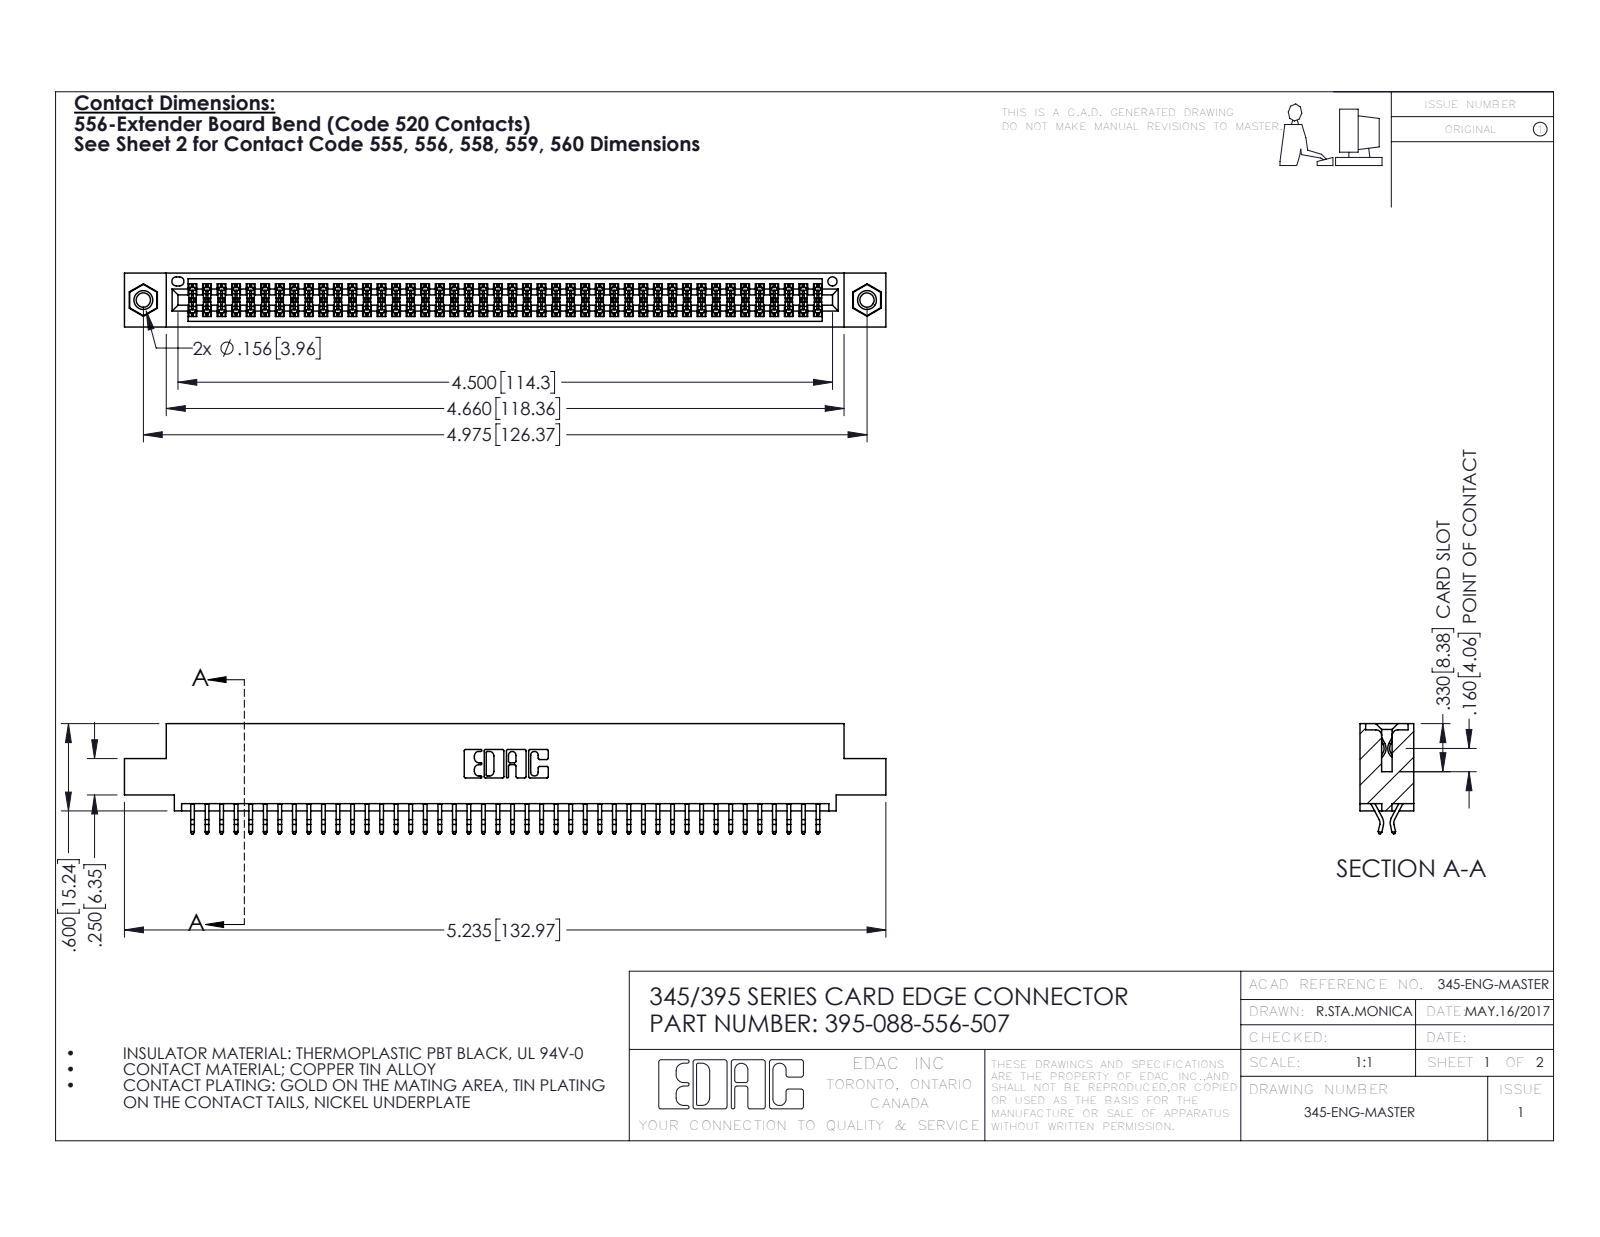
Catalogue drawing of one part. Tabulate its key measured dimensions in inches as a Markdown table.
| quantity | value |
| --- | --- |
| part name | 395-088-556-507; 345-292-001_556 Tail; 345-250-001_345-250-005-103; 345 Part_0.110 Offset - 0.156 Dia-TI |
| STEP written by | SolidWorks 2016 (CONFIG_CONTROL_DESIGN) |
| units | inches |
| bodies | 91 solids, 5118 faces (3372 planar, 1730 cylindrical, 16 other) |
| overall size | 5.235 × 0.757 × 0.37 |
| volume | 0.784 in³ |
| surface area | 29.56 in² |
| round holes (diameter × count) | 0.098 × 2, 0.125 × 2, 0.156 × 2, 0.064 × 1 |
| round bosses / shafts (diameter × count) | 0.155 × 2 |
| partial cylindrical surfaces (radius × count) | 0.006 × 132, 0.01 × 22, 0.007 × 6, 0.031 × 6, 0.026 × 3, 0.01 × 2, 0.014 × 2, 0.019 × 2 |
| main face-to-face distances | 0.072, 0.298, 0.37, 0.2, 0.025, 0.098, 0.272, 0.225, 0.175, 0.149 |
| hole center spacings | 0.27, 4.739, 4.975 |
